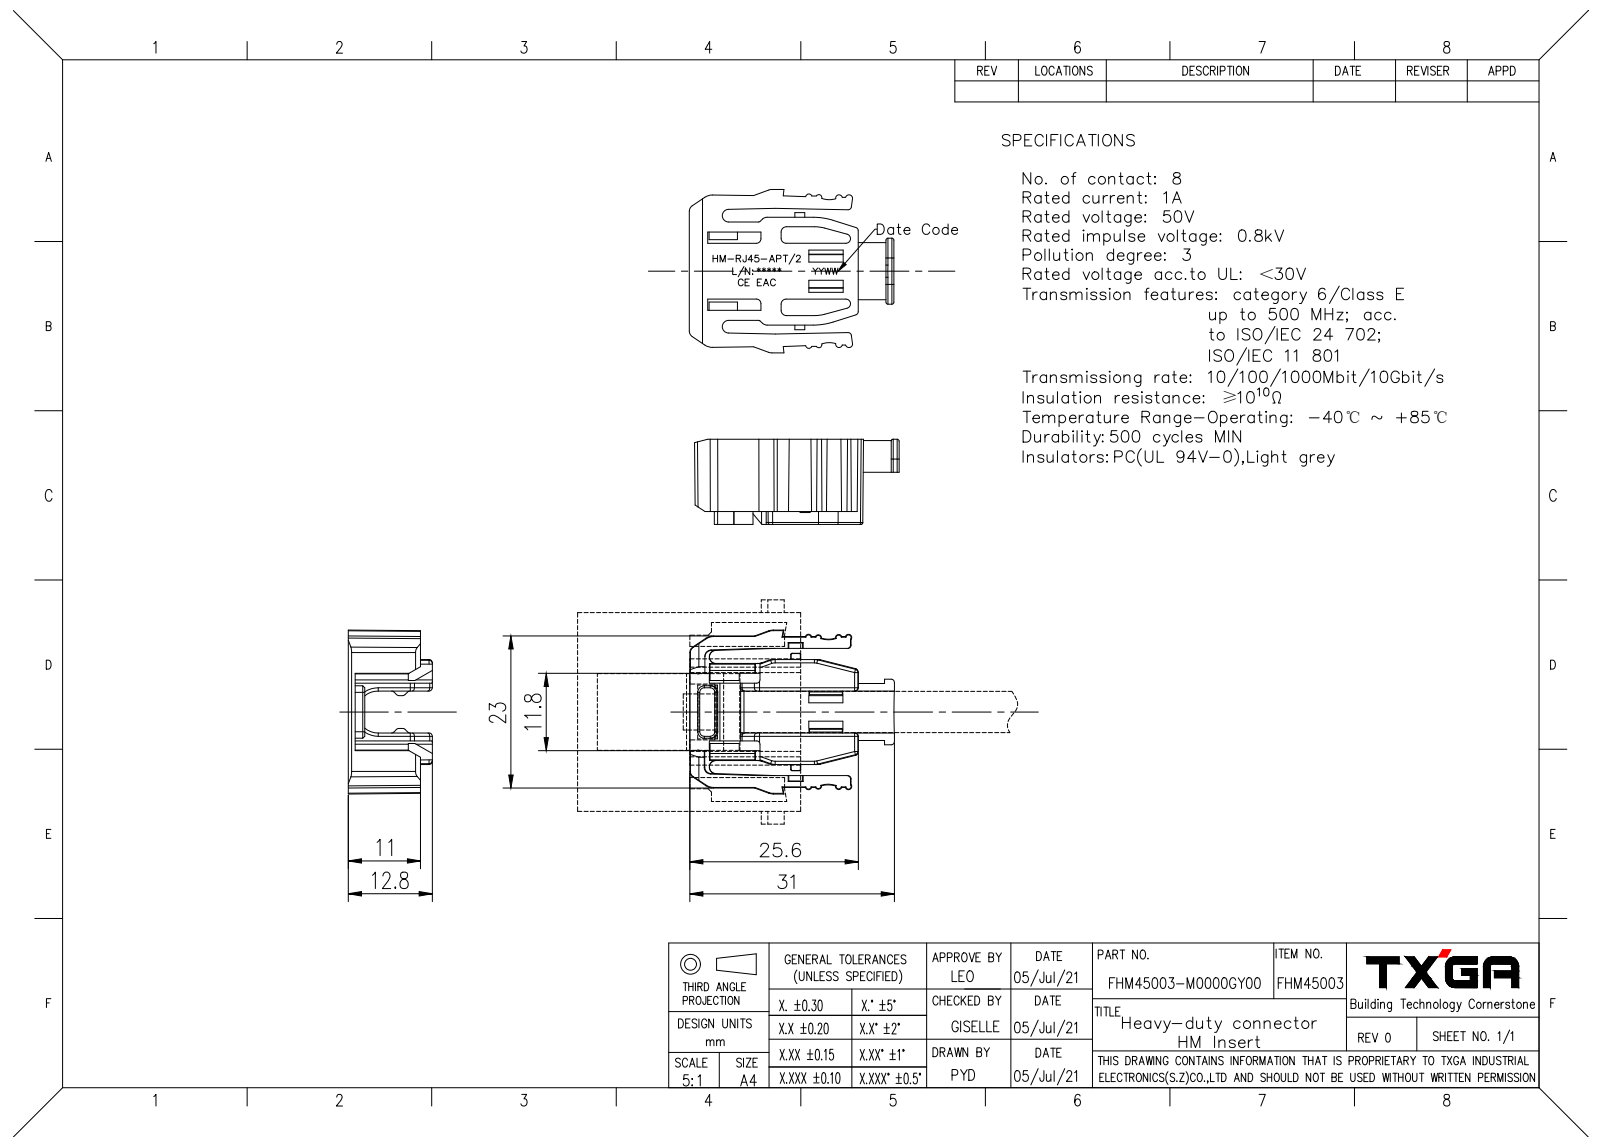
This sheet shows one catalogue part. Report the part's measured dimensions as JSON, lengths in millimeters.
{"part_name": "FHM45003-M0000GY00", "step_written_by": "SolidWorks 2021 (CONFIG_CONTROL_DESIGN)", "units": "millimeters", "bodies": {"solids": 1, "faces": 201, "planar": 135, "cylindrical": 52, "other": 14}, "overall_size": [31.2, 24.5, 12.8], "volume_mm3": 3240, "surface_area_mm2": 4516, "partial_cylinders_radius": [[0.2, 13], [0.5, 10], [0.25, 8], [1, 8], [0.95, 4], [2, 2], [3.25, 1], [4.25, 1]], "face_to_face_distances": [4.9, 15.8, 3.7, 1.2, 5.85, 12.35, 2.5, 13.3, 0.95, 7.45]}
